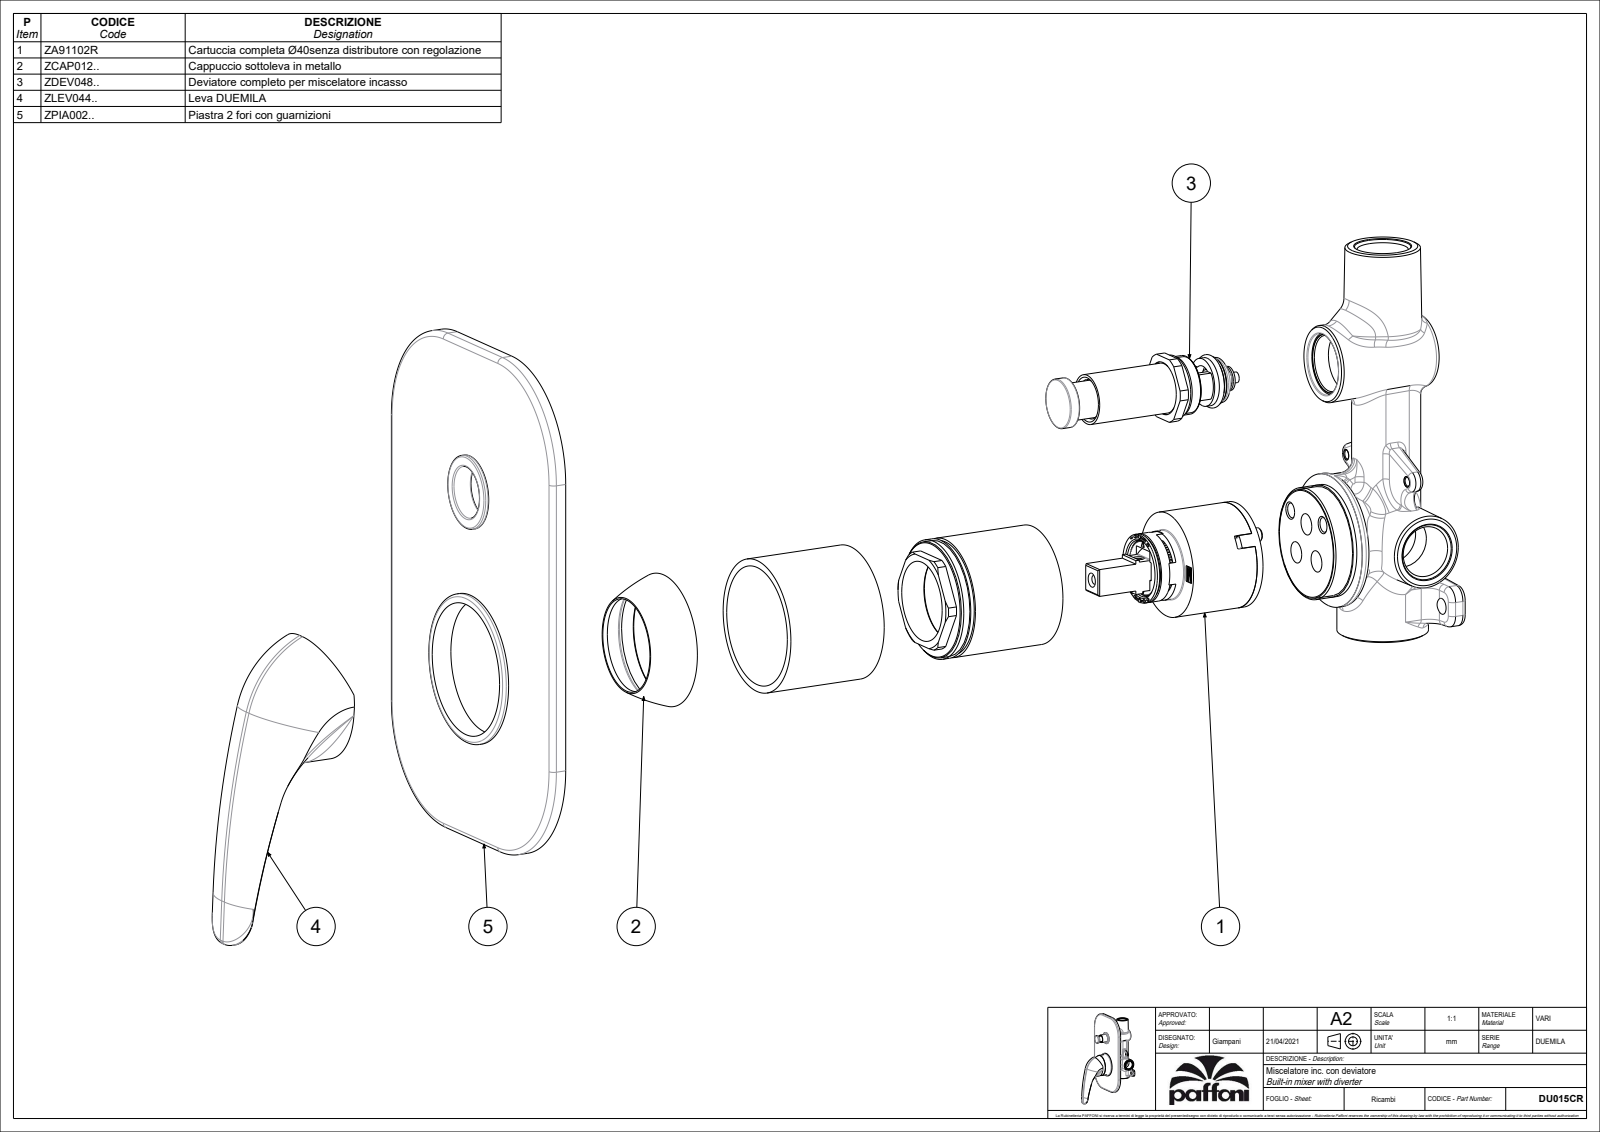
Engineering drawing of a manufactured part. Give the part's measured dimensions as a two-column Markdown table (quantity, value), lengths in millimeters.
| quantity | value |
| --- | --- |
| part name | DU015CR |
| STEP written by | CREO PARAMETRIC BY PTC INC, 2020044 (CONFIG_CONTROL_DESIGN) |
| units | millimeters |
| bodies | 1 solid, 108 faces (26 planar, 38 cylindrical, 44 other) |
| overall size | 215.67 × 120.5 × 72.72 |
| volume | 231 436 mm³ |
| surface area | 65 957 mm² |
| round holes (diameter × count) | 4.5 × 1, 9.2 × 1 |
| round bosses / shafts (diameter × count) | 56.5 × 1, 50.3 × 1, 27.7 × 1, 18.7 × 1, 18.6 × 1, 18.1 × 1, 14 × 1 |
| partial cylindrical surfaces (radius × count) | 2 × 4, 40 × 4, 1.5 × 2, 15 × 2, 24 × 2, 24.5 × 2, 18 × 1, 39.04 × 1 |
| main face-to-face distances | 6, 39.2, 33.2, 8, 2, 31.2, 120.5, 55.2, 65.3, 190 |
